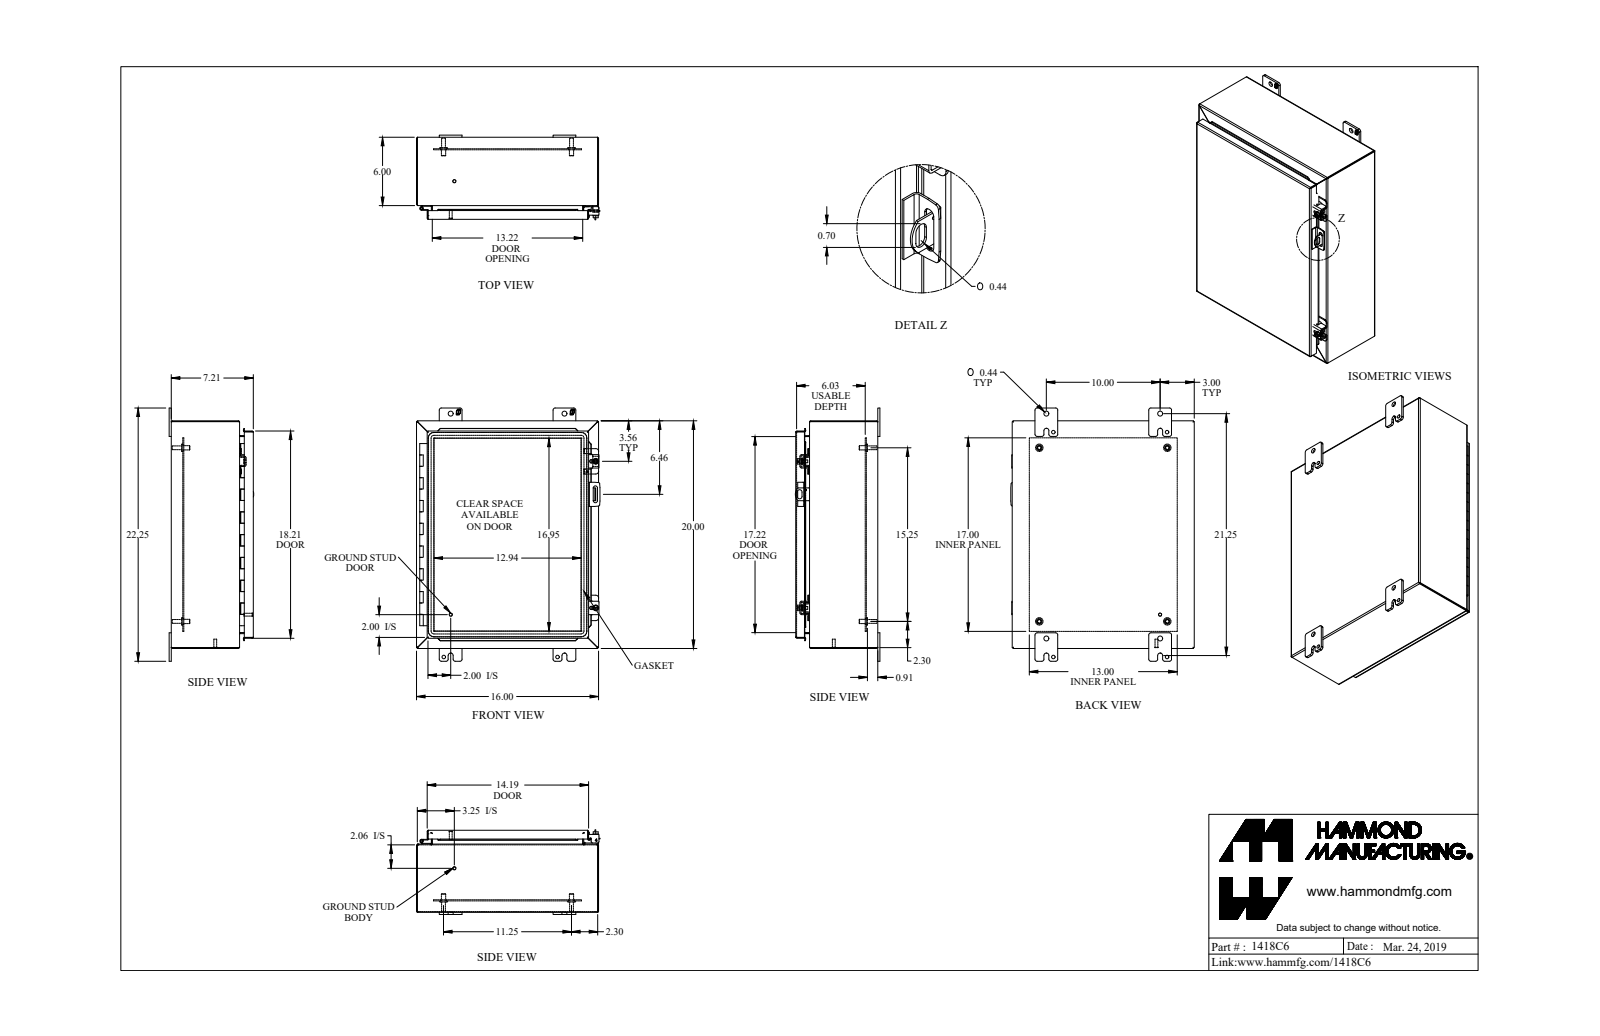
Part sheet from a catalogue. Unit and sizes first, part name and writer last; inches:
Units: inches
Overall size (bounding box): 22.25 × 16.125 × 7.437
Round holes (diameter × count): ⌀0.313 ×4, ⌀0.437 ×4, ⌀0.5 ×4, ⌀0.213 ×2, ⌀0.265 ×2, ⌀0.307 ×2, ⌀0.375 ×2, ⌀0.445 ×2, ⌀0.125 ×1, ⌀0.187 ×1
Round bosses / shafts (diameter × count): ⌀0.65 ×4, ⌀0.375 ×4, ⌀0.33 ×4, ⌀1 ×2, ⌀0.5 ×2, ⌀0.39 ×2, ⌀0.281 ×2, ⌀0.25 ×2
Partial cylindrical surfaces — rounded edges, fillets, slot ends (radius × count): R0.188 ×26, R0.036 ×20, R0.108 ×20, R0.048 ×13, R0.143 ×13, R0.007 ×8, R0.045 ×8, R0.079 ×8
Main face-to-face distances: 0.072, 7.113, 7.041, 0.937, 7.185, 1.009, 15.928, 0.095, 6.081, 6.009
Hole centre spacings: 1.735, 10, 19.75, 22.137, 2.434, 14.223, 15.25, 18.261
Volume: 125.6 in³ · Surface area: 3 250 in²
Bodies: 38 solids, 970 faces (667 planar, 251 cylindrical, 52 other)
Part name (STEP PRODUCT): 1418C6
STEP written by: SolidWorks 2019 (AUTOMOTIVE_DESIGN)
